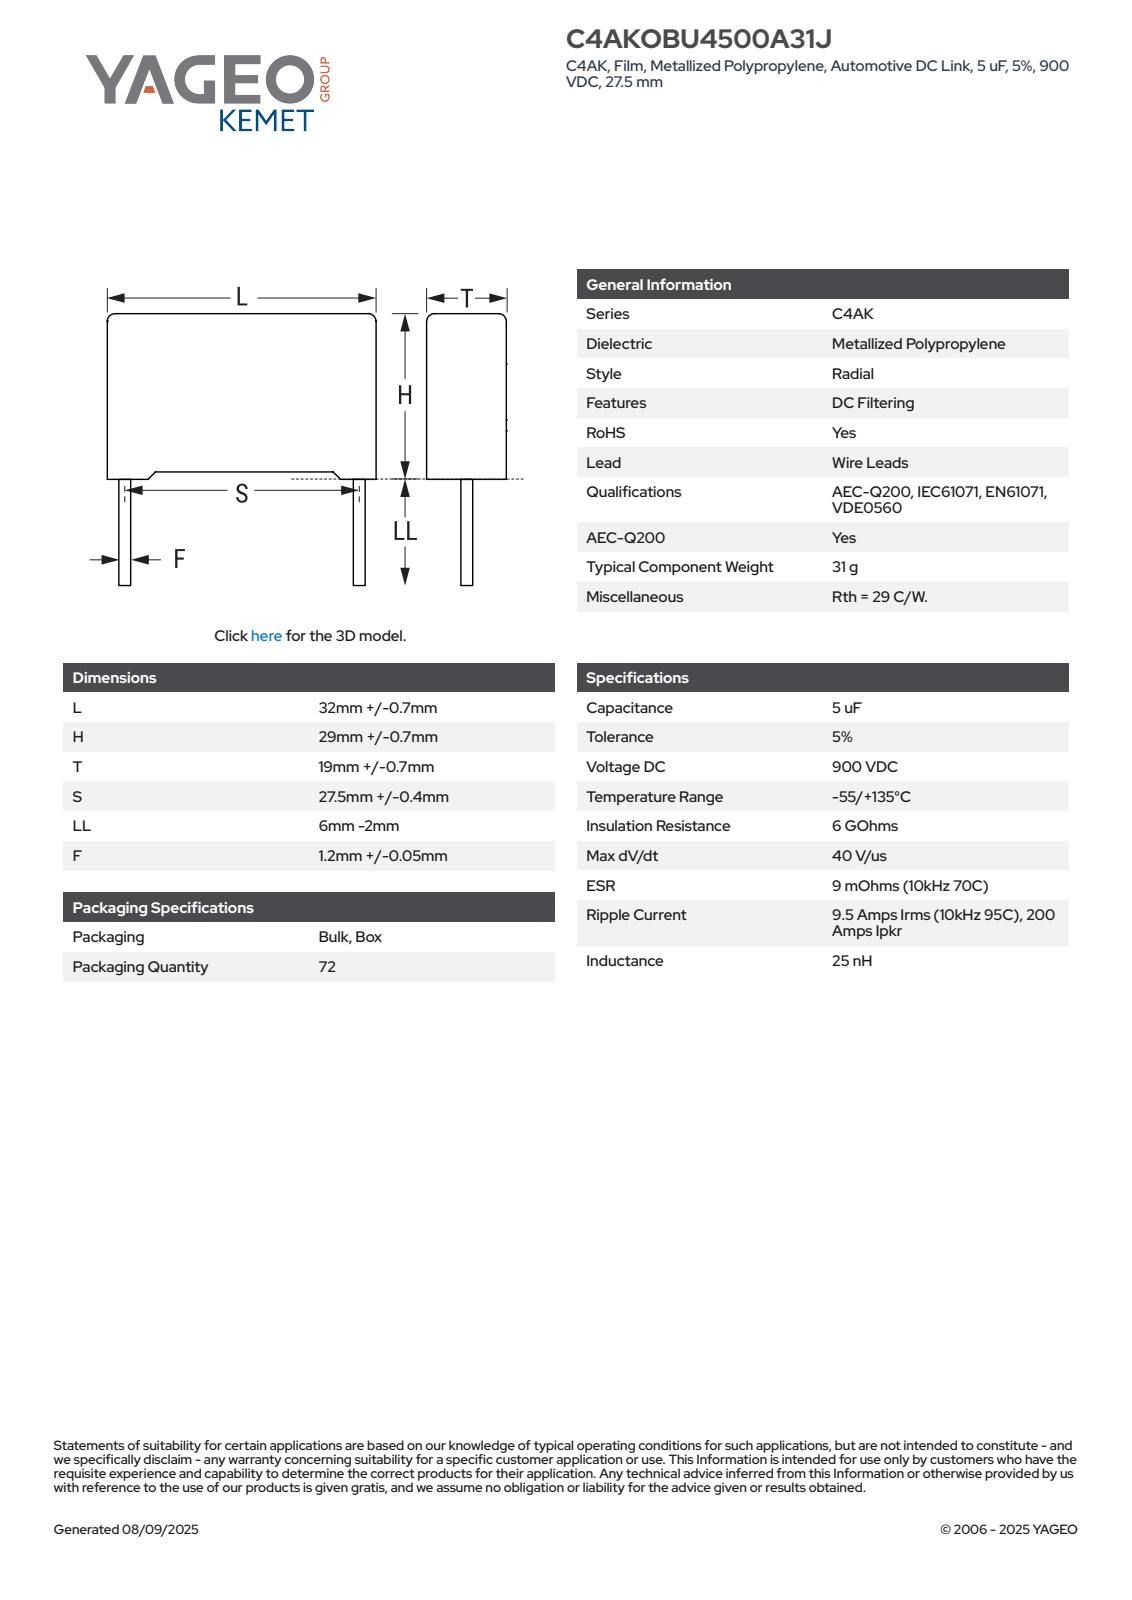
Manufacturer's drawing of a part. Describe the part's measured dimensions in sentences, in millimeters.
The part is named "CFR_RB2CFP_32X29X19_L32.7H29.7T19.7S27.5LL4F1.25". Its 3-D file was written by "SolidWorks 2014 (AUTOMOTIVE_DESIGN)". It is 4 solids with 85 faces: 77 planar, 8 cylindrical and 0 other. Overall it measures 33.7 by 32.7 by 19.7 millimeters. Its volume is 18 575 cubic millimeters and its surface area 4 490 square millimeters. Round bosses or shafts: 2 of diameter 1.25. Partial cylindrical surfaces (rounded edges, fillets, slot ends): 4 of radius 0.5. The main face-to-face distances are 19.7, 32.7, 28.68, 28.95, 0.75, 1.02, 29.7, 1.09, 31.61, 19.71.
